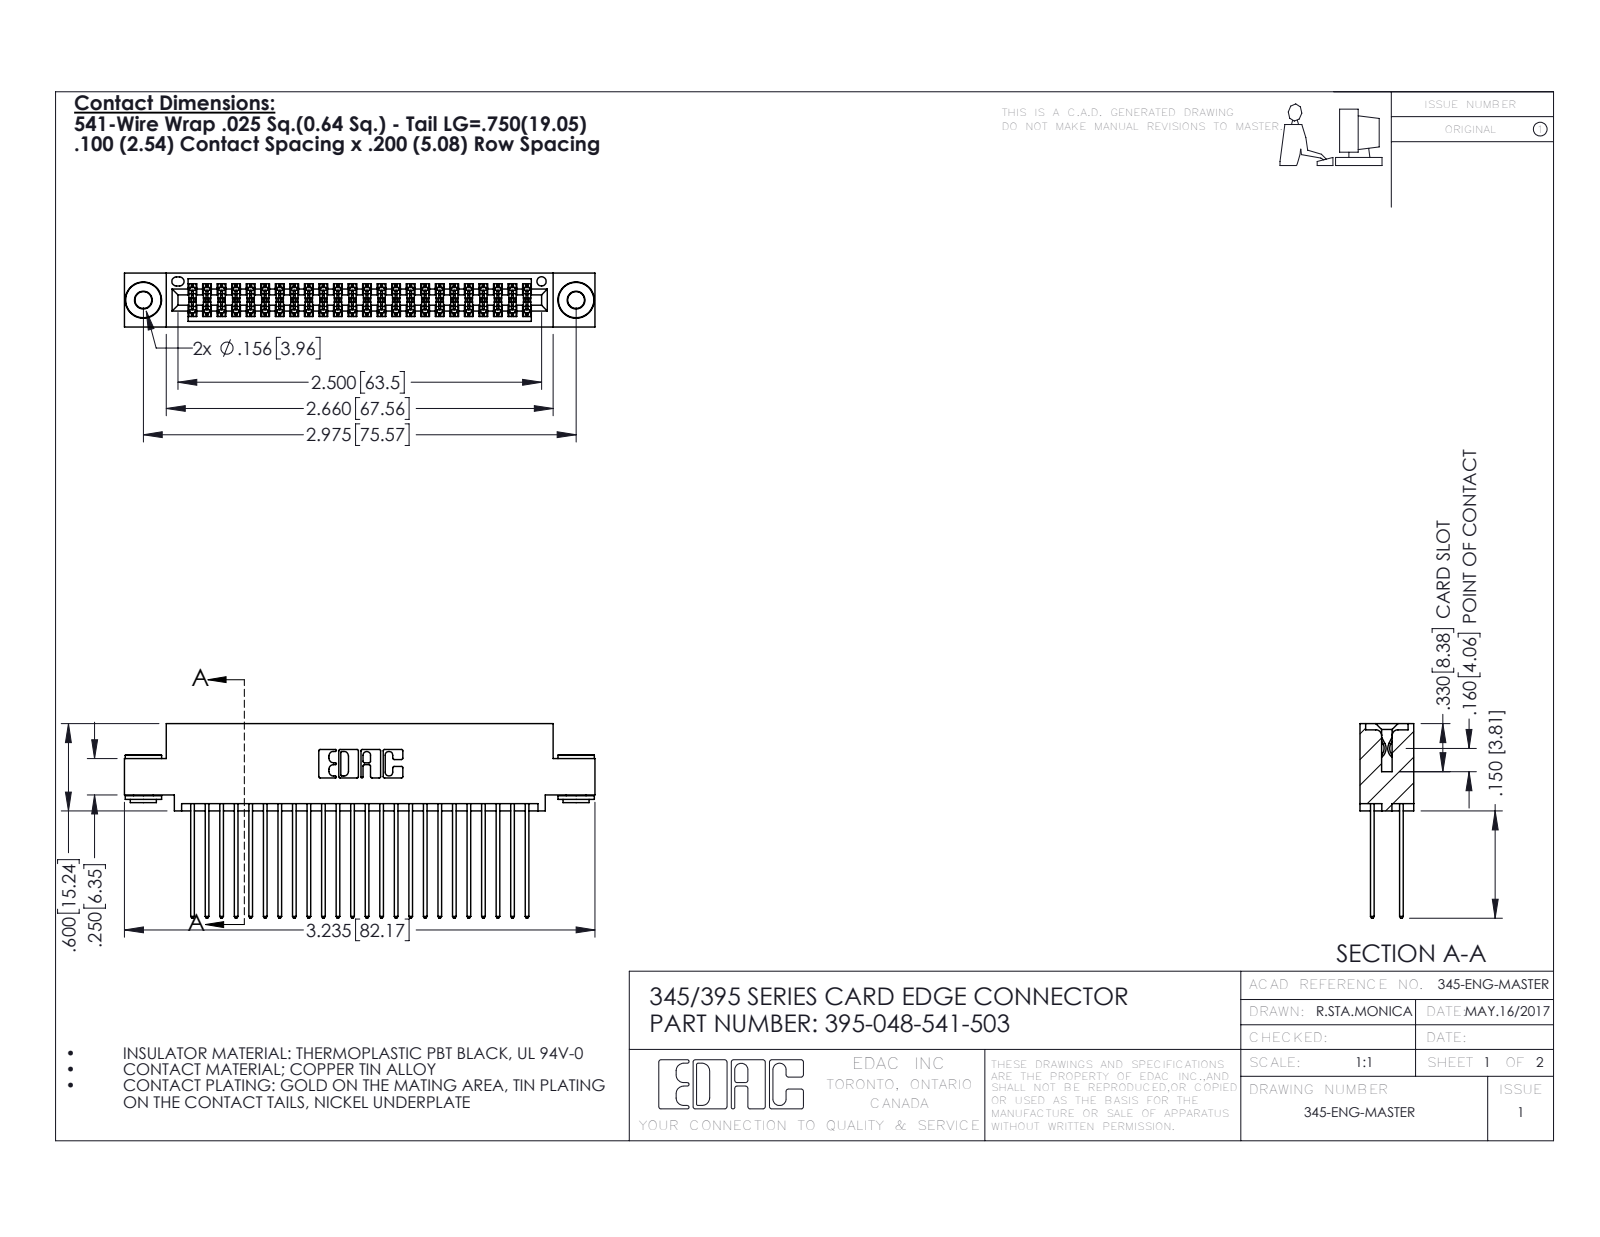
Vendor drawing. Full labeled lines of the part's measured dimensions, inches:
Part name (STEP PRODUCT): 345-250-002_345-250-002-102; 345 Part_0.110 Offset - 0.156 Dia-TH; 395-048-541-503; 345-292-001_345-293-141
STEP written by: SolidWorks 2016 (CONFIG_CONTROL_DESIGN)
Units: inches
Bodies: 51 solids, 2568 faces (1678 planar, 882 cylindrical, 8 other)
Overall size (bounding box): 3.235 × 1.337 × 0.37
Volume: 0.49 in³ · Surface area: 20.34 in²
Round holes (diameter × count): ⌀0.116 ×2, ⌀0.156 ×2, ⌀0.064 ×1
Round bosses / shafts (diameter × count): ⌀0.25 ×2, ⌀0.18 ×2, ⌀0.136 ×2
Partial cylindrical surfaces — rounded edges, fillets, slot ends (radius × count): R0.006 ×72, R0.01 ×48, R0.01 ×22, R0.007 ×6, R0.031 ×6, R0.026 ×3, R0.014 ×2, R0.019 ×2
Main face-to-face distances: 0.072, 0.298, 0.2, 0.025, 0.098, 0.272, 0.37, 0.225, 0.175, 0.149
Hole centre spacings: 0.27, 2.741, 2.975
